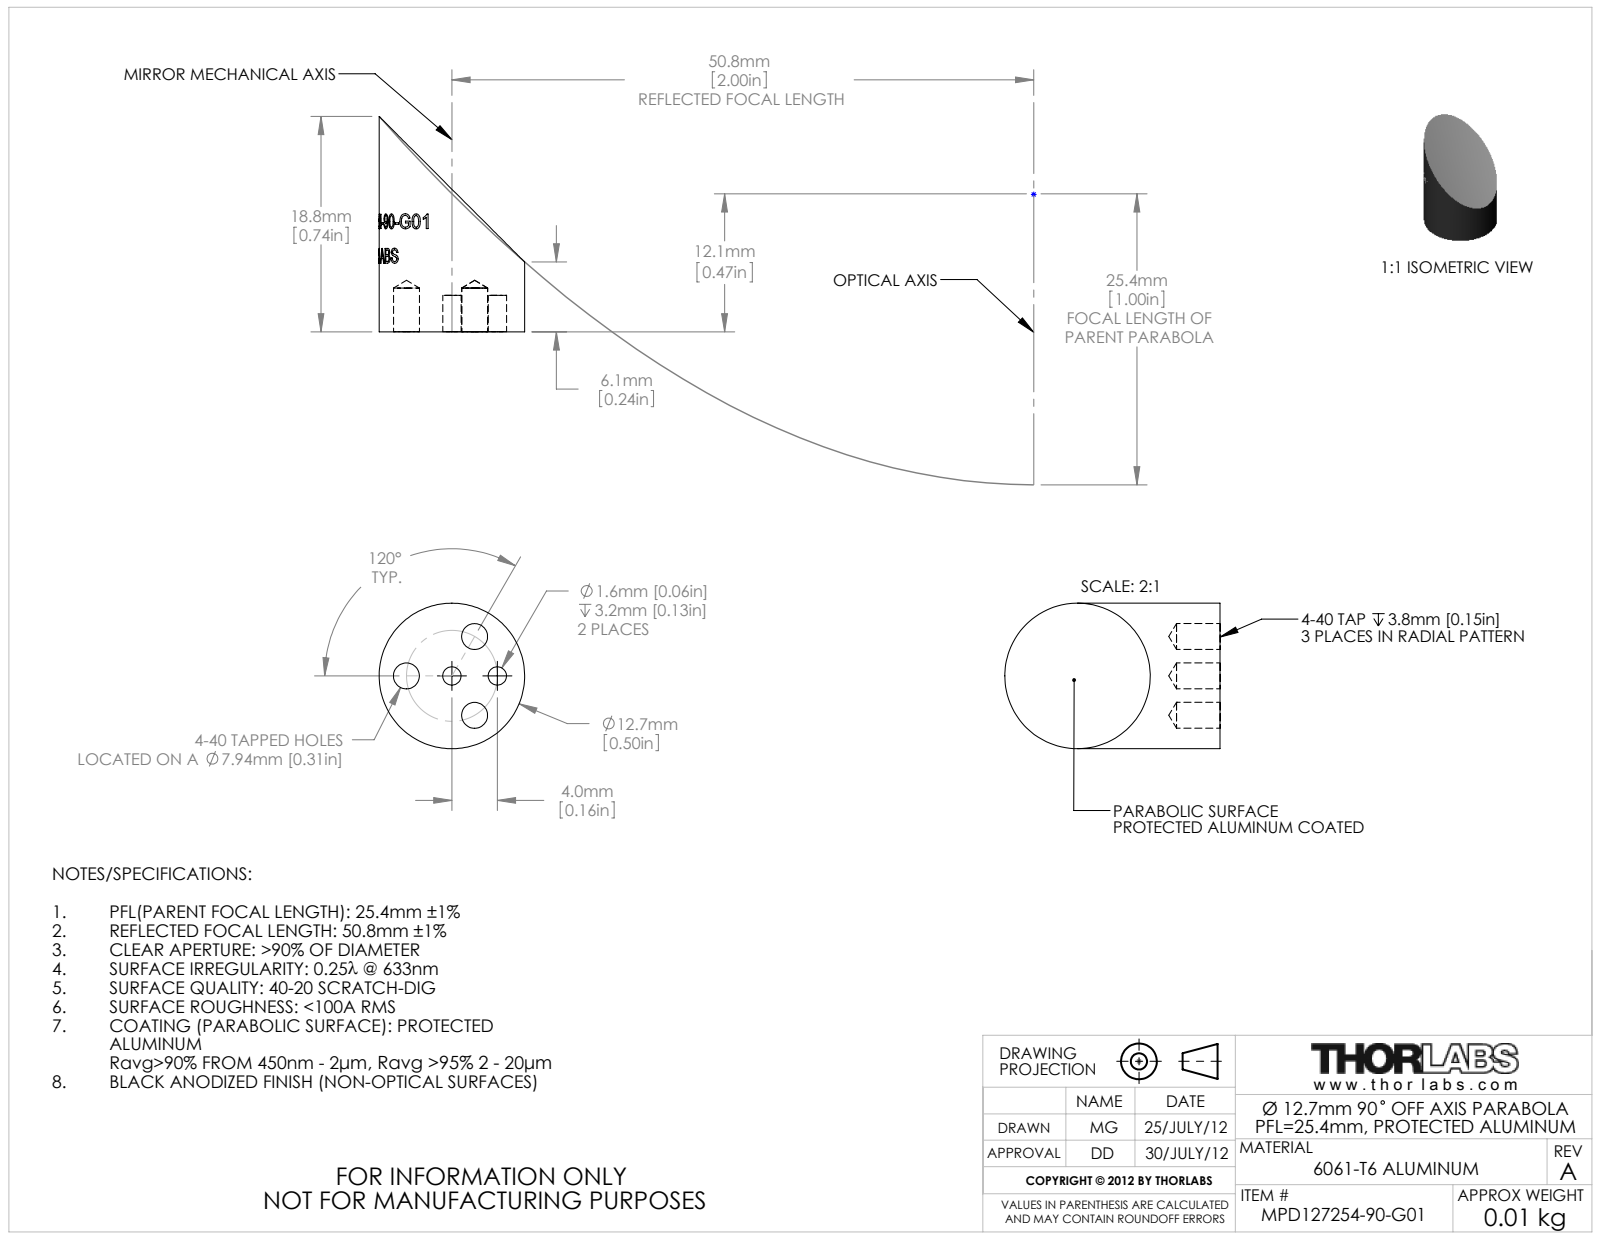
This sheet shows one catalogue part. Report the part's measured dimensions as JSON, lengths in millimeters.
{"part_name": "24694-E0W", "step_written_by": "SolidWorks 2012 (CONFIG_CONTROL_DESIGN)", "units": "millimeters", "bodies": {"solids": 1, "faces": 58, "planar": 3, "cylindrical": 47, "other": 8}, "overall_size": [18.8, 12.7, 12.7], "volume_mm3": 1490, "surface_area_mm2": 918, "round_holes": [[2.26, 3], [1.6, 2]], "round_bosses_or_shafts": [[12.7, 1]], "face_to_face_distances": [3.17], "hole_center_spacings": [3.97, 6.87, 6.88, 7.94]}
